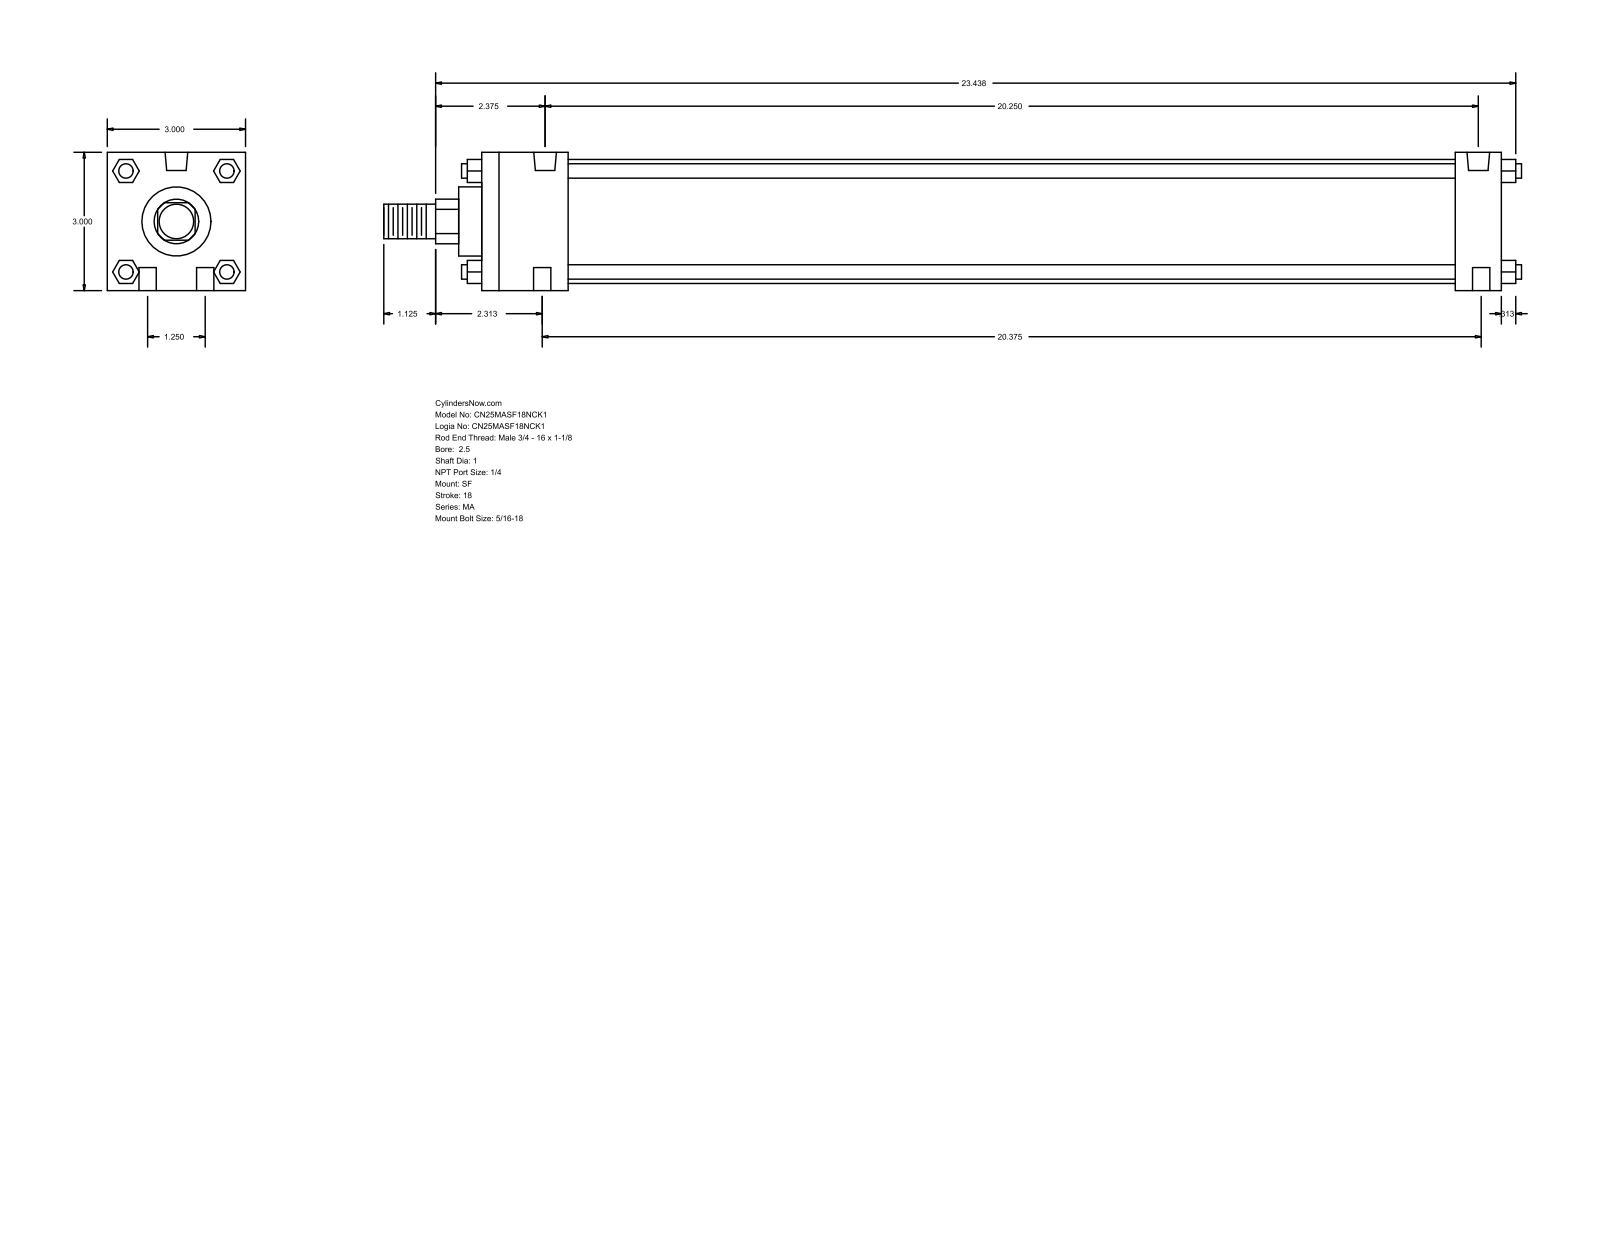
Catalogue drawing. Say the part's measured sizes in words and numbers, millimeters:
The part is named "MA_SF__0250_1". Its 3-D file was written by "GSSL Pune (CONFIG_CONTROL_DESIGN)". It is 0 solids with 124 faces: 94 planar, 30 cylindrical and 0 other. Overall it measures 627.06 by 76.2 by 76.2 millimeters. Round holes: 4 of diameter 9.53, 2 of diameter 7.94, 2 of diameter 12.49. Round bosses or shafts: 4 of diameter 7.94, 1 of diameter 68.33, 1 of diameter 38.1, 1 of diameter 25.4, 1 of diameter 19.05. Partial cylindrical surfaces (rounded edges, fillets, slot ends): 1 of radius 12.29. The main face-to-face distances are 76.2, 561.98, 12.7, 25.4, 536.58, 47.63, 488.95, 514.35, 27.81, 48.17. The hole center spacings are 15.96, 516.17, 31.76, 514.34, 517.52, 518.49.
